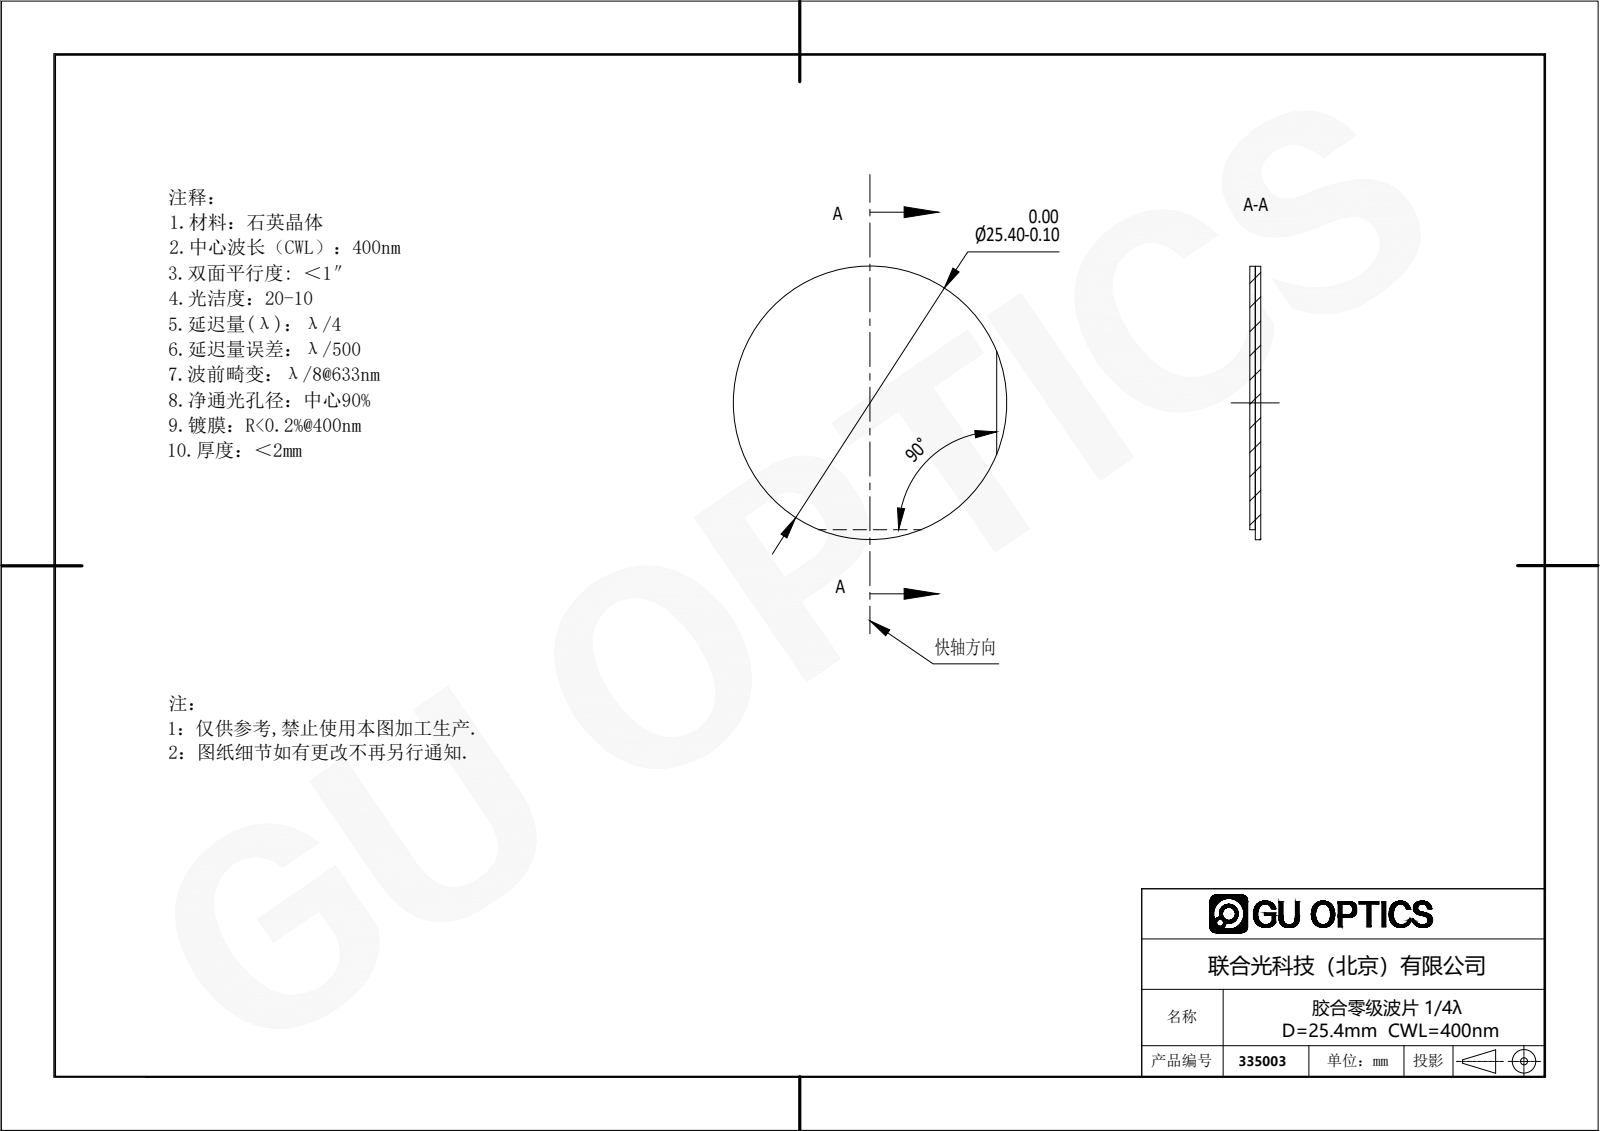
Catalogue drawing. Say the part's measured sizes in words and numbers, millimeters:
The part is named "334001". Its 3-D file was written by "SolidWorks 2019 (AUTOMOTIVE_DESIGN)". It is 2 solids with 12 faces: 6 planar, 6 cylindrical and 0 other. Overall it measures 25.4 by 25.4 by 1 millimeters. Its volume is 501 cubic millimeters and its surface area 2 082 square millimeters. Round bosses or shafts: 1 of diameter 25.4. The main face-to-face distances are 0.5, 1.
